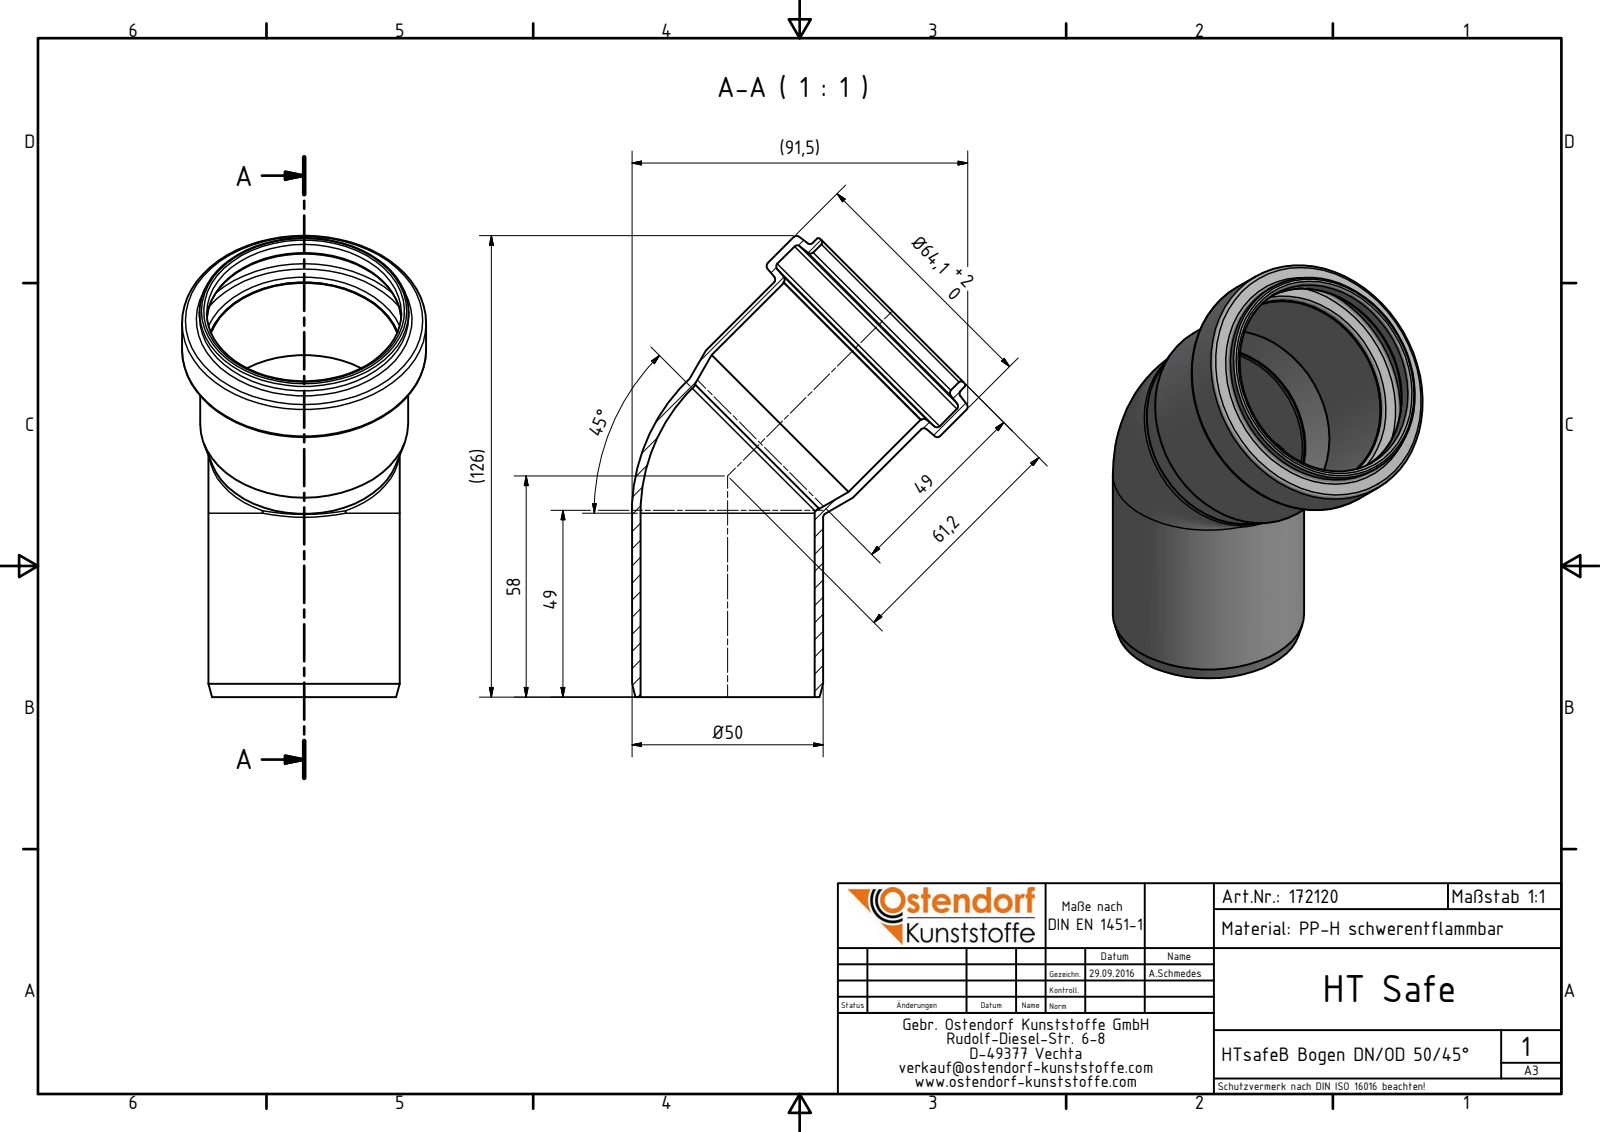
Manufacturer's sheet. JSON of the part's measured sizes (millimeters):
{"part_name": "172120 HTsafeB DN_OD 50_45°", "step_written_by": "Autodesk Inventor 2016 (AUTOMOTIVE_DESIGN)", "units": "millimeters", "bodies": {"solids": 1, "faces": 35, "planar": 4, "cylindrical": 11, "other": 20}, "overall_size": [121.06, 88.16, 64.1], "volume_mm3": 41997, "surface_area_mm2": 40740, "round_holes": [[45.69, 2], [50.8, 1], [51.1, 1], [60.3, 1]], "round_bosses_or_shafts": [[50.2, 2], [64.1, 1], [54.9, 1], [54.6, 1]], "face_to_face_distances": [50.28, 35.38, 14.9]}
